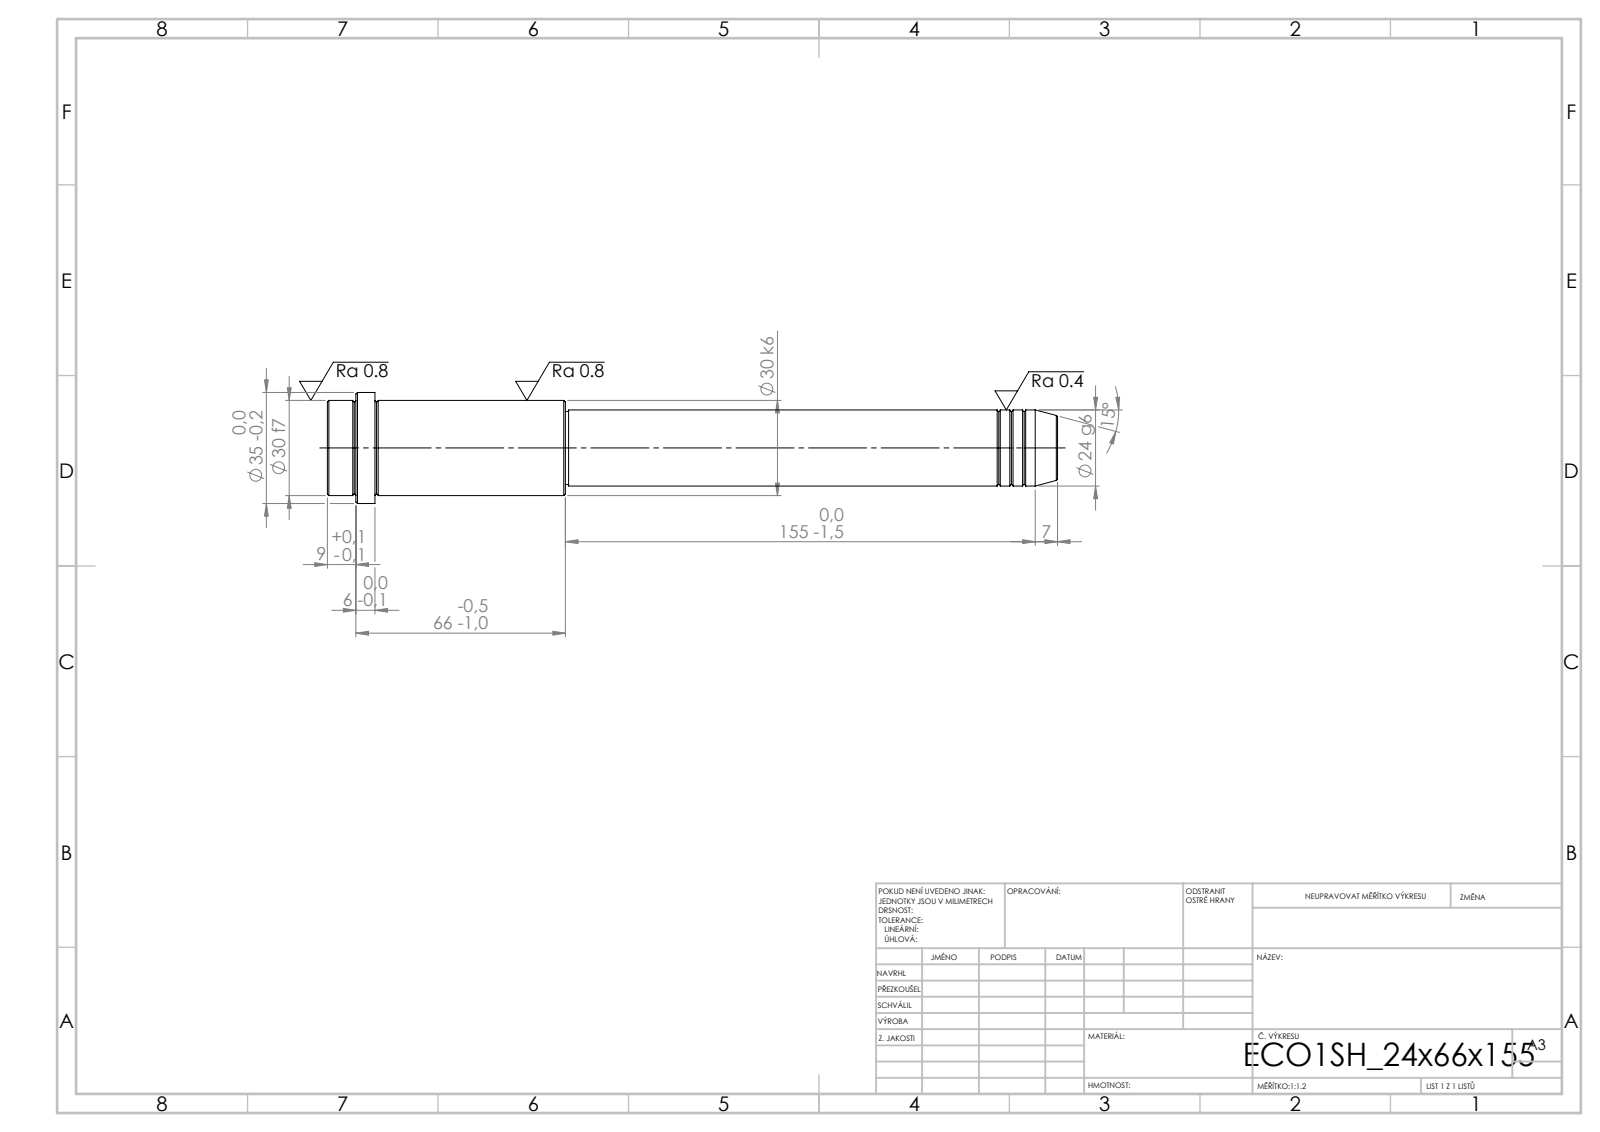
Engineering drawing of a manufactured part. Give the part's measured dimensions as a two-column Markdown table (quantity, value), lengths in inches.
| quantity | value |
| --- | --- |
| STEP written by | SolidWorks 2019 (CONFIG_CONTROL_DESIGN) |
| units | inches |
| bodies | 1 solid, 52 faces (6 planar, 16 cylindrical, 30 other) |
| overall size | 9.055 × 1.378 × 1.378 |
| volume | 7.565 in³ |
| surface area | 32.26 in² |
| round bosses / shafts (diameter × count) | 1.378 × 1, 1.181 × 1, 0.945 × 1, 0.906 × 1 |
| main face-to-face distances | 9.055, 8.465, 0.591, 6.102, 2.362, 2.953, 8.701, 2.598, 0.236, 0.354 |
